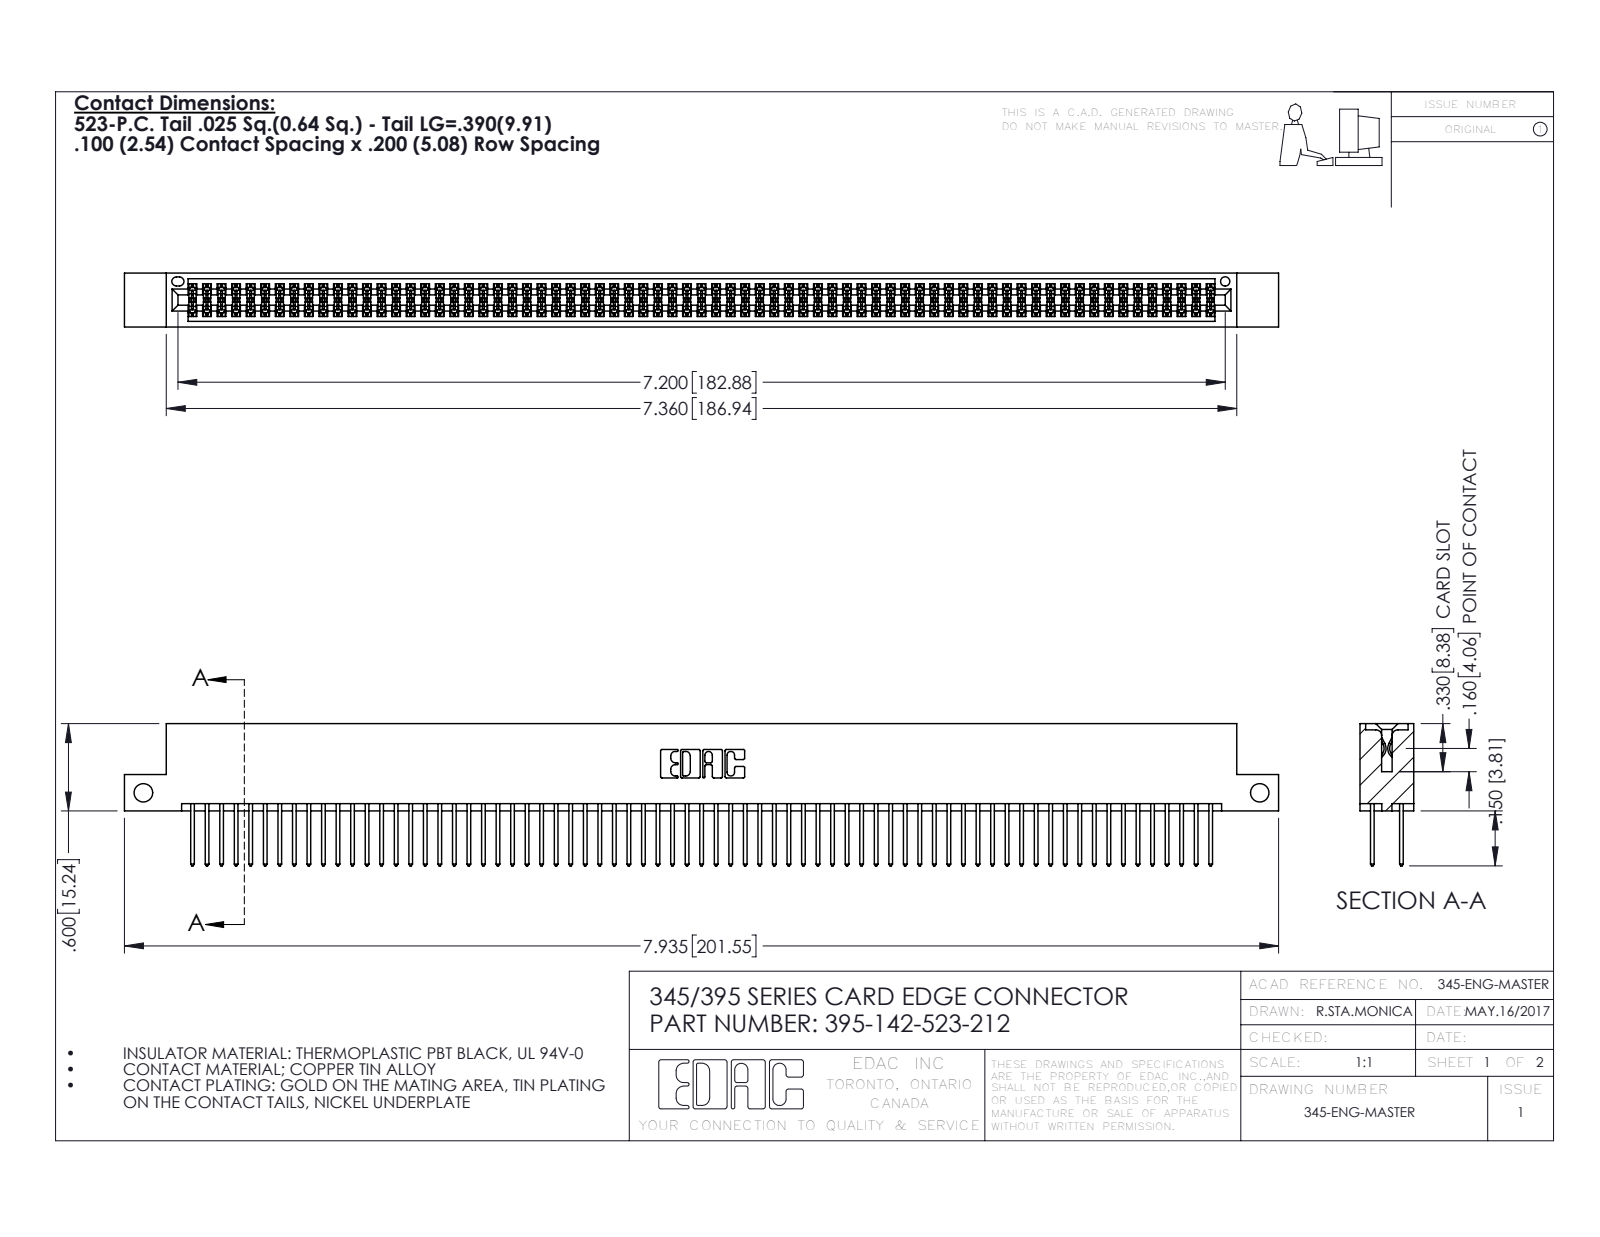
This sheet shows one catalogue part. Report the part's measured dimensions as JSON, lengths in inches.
{"part_name": "395-142-523-212; 345 Part_Flush Mounting Lugs - Side Mount; 345-292-001_345-293-123", "step_written_by": "SolidWorks 2016 (CONFIG_CONTROL_DESIGN)", "units": "inches", "bodies": {"solids": 143, "faces": 7226, "planar": 4766, "cylindrical": 2460, "other": 0}, "overall_size": [7.935, 0.977, 0.37], "volume_in3": 1.224, "surface_area_in2": 48.63, "round_holes": [[0.128, 2], [0.064, 1]], "partial_cylinders_radius": [[0.006, 213], [0.01, 142], [0.01, 22], [0.007, 6], [0.031, 6], [0.026, 3], [0.014, 2], [0.019, 2]], "face_to_face_distances": [0.298, 0.072, 0.2, 0.098, 0.272, 0.025, 0.37, 0.225, 0.175, 0.149], "hole_center_spacings": [7.675]}
